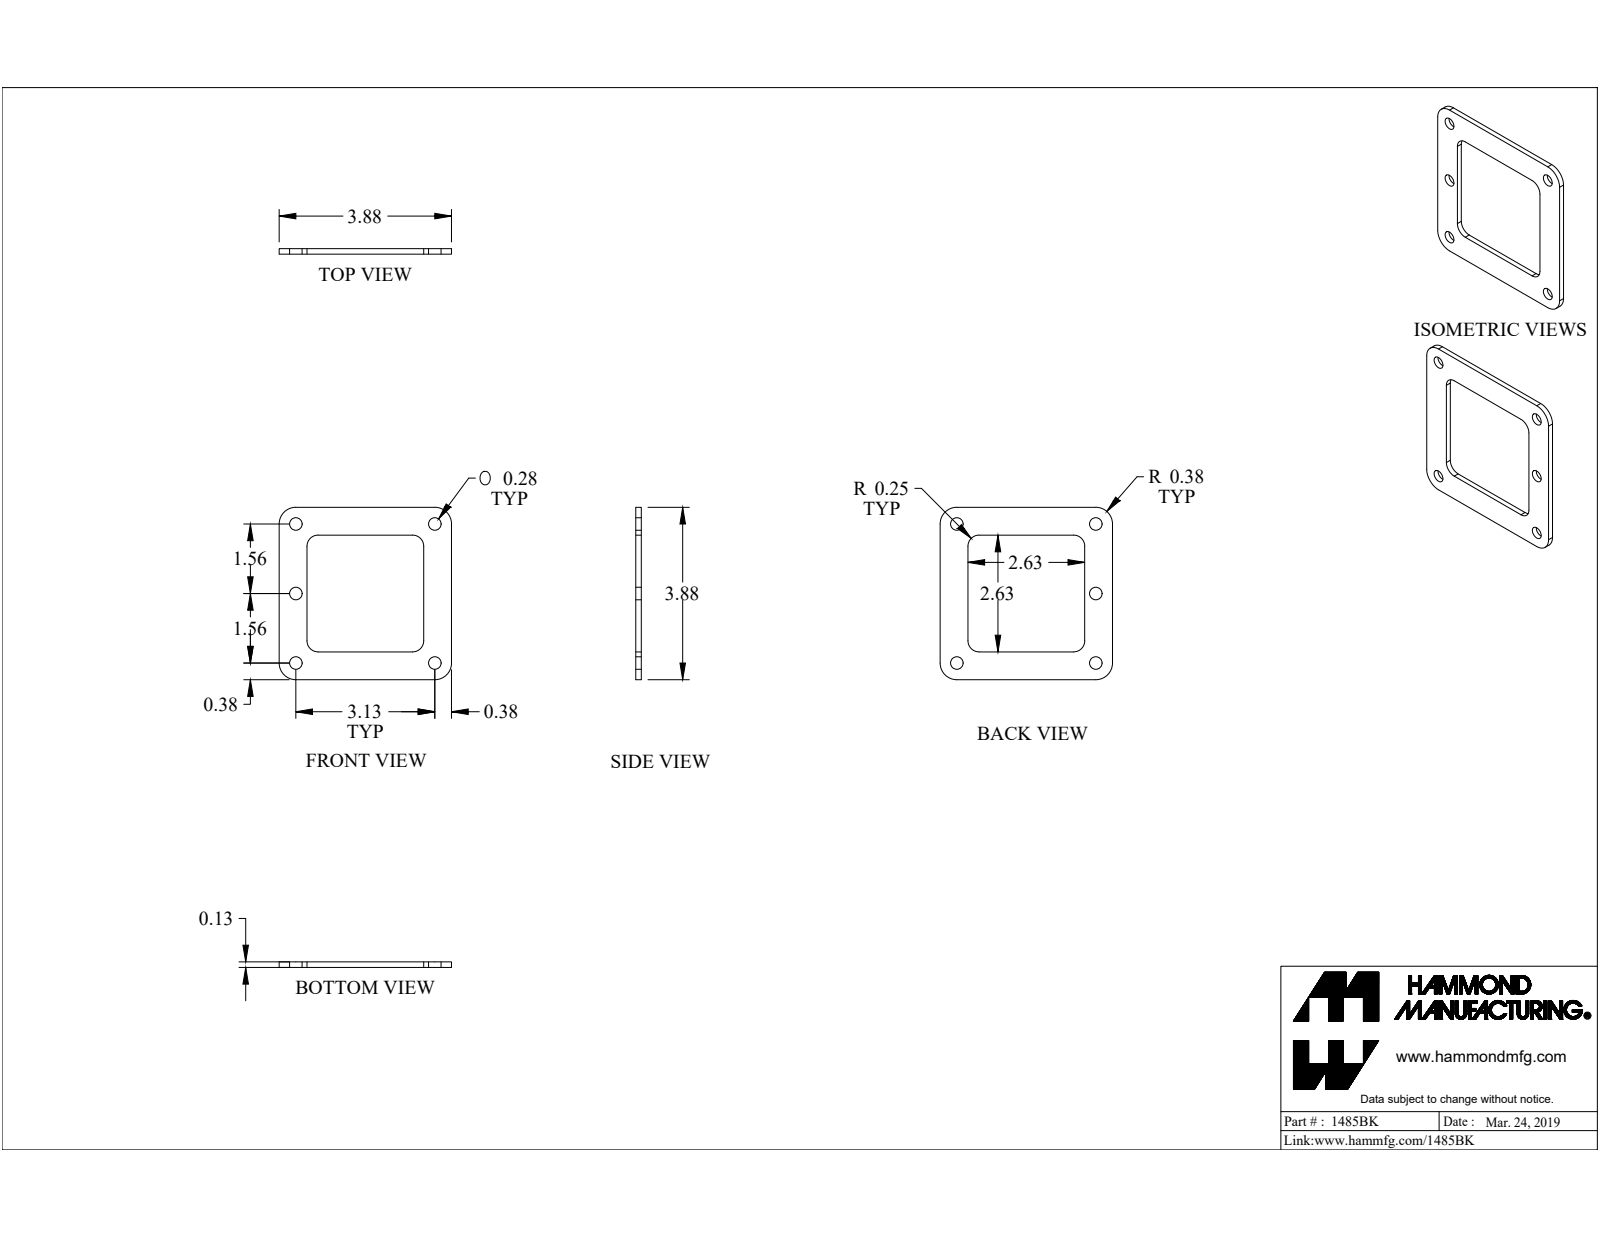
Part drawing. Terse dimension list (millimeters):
name: 1485BK
written by: SolidWorks 2019 (CONFIG_CONTROL_DESIGN)
unit: mm
bodies: 1 solid, 23 faces (10 planar, 13 cylindrical, 0 other)
size: 98.4 × 98.4 × 3.2
volume: 15 900 mm³; area: 12 360 mm²
holes: 5× ⌀7.1
rounds: 4× R6.4, 4× R9.5
face distances: 3.2, 15.9, 82.6, 98.4, 66.7
hole spacings: 79.4, 39.7, 88.7, 112.3
